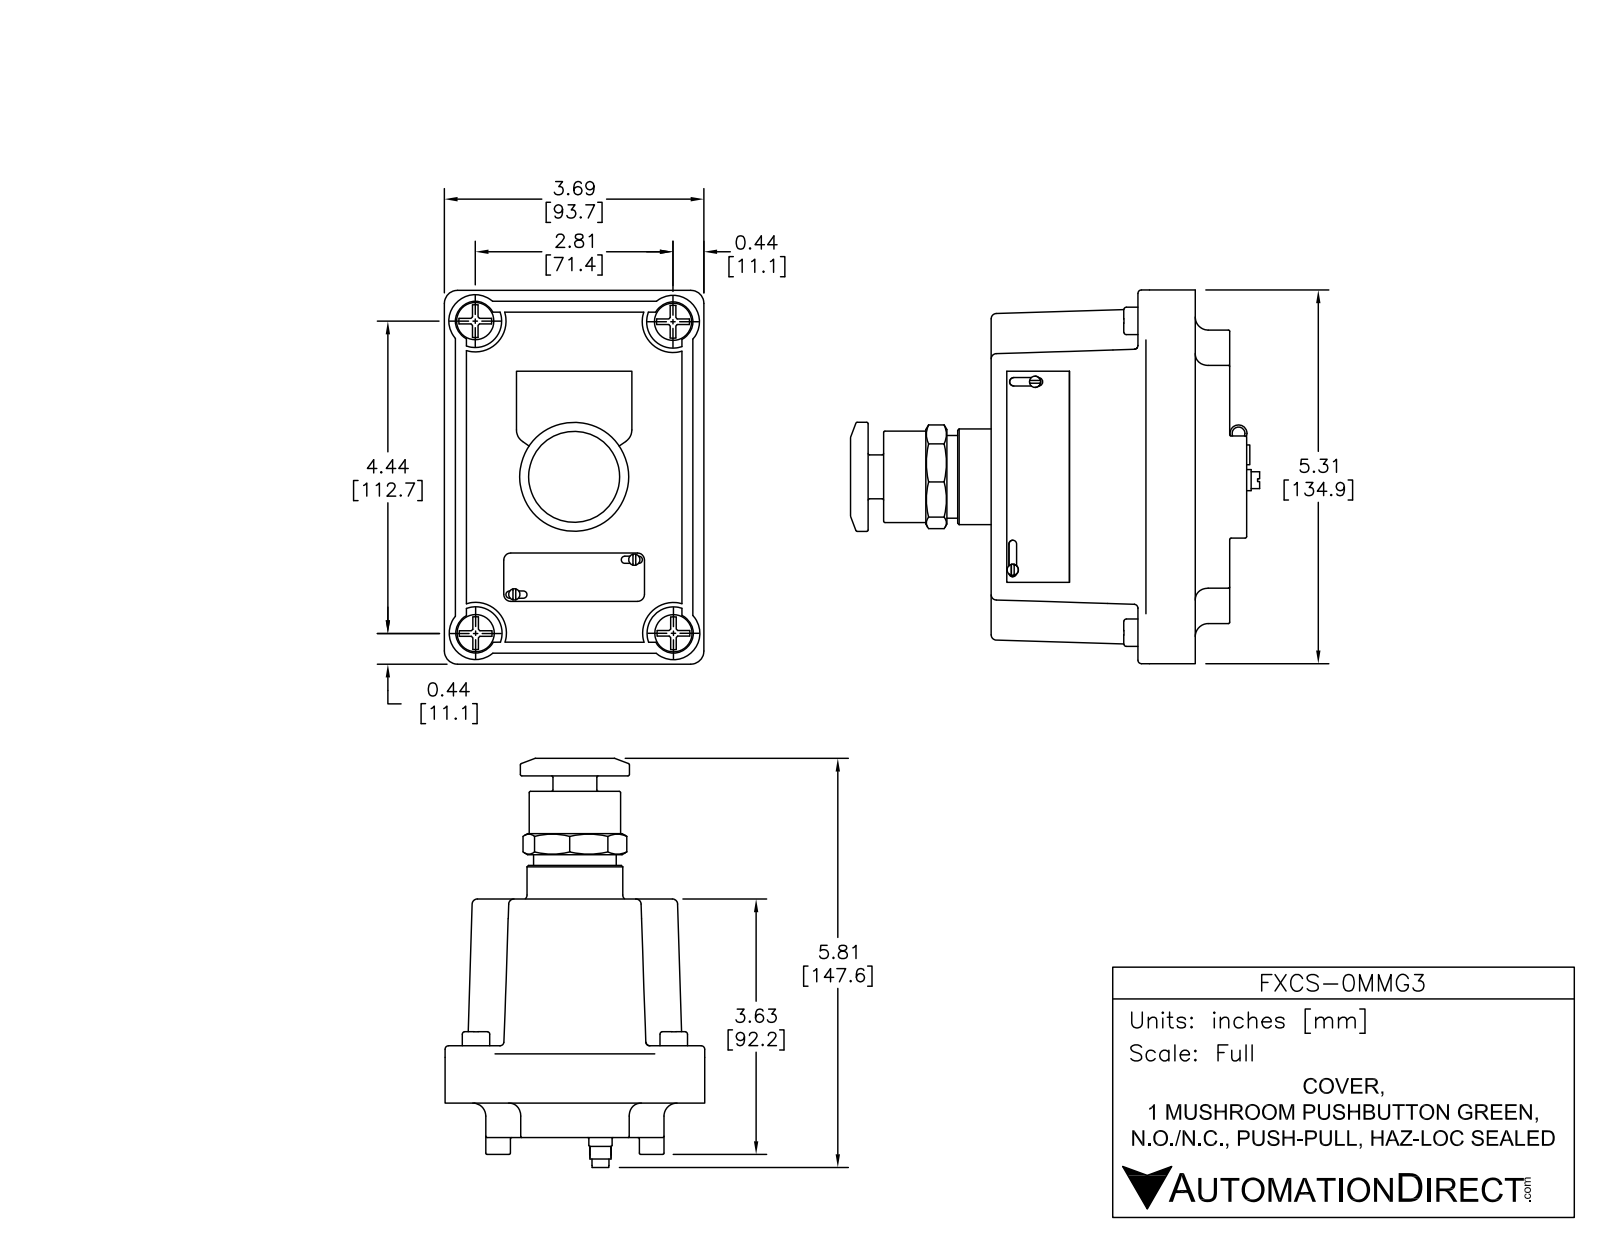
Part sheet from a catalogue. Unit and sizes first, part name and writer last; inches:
Units: inches
Overall size (bounding box): 5.814 × 5.31 × 3.69
Round holes (diameter × count): ⌀0.16 ×8, ⌀0.198 ×1
Round bosses / shafts (diameter × count): ⌀0.16 ×6, ⌀0.39 ×4, ⌀1.55 ×1, ⌀1.36 ×1, ⌀1.3 ×1, ⌀1.175 ×1, ⌀0.623 ×1, ⌀0.33 ×1
Partial cylindrical surfaces — rounded edges, fillets, slot ends (radius × count): R0.02 ×22, R0.05 ×12, R0.051 ×4, R0.055 ×4, R0.06 ×4, R0.075 ×4, R0.1 ×4, R0.185 ×4
Main face-to-face distances: 0.49, 3.39, 2.9, 0.02, 3.69, 0.578, 3.111, 1.19, 0.7, 2.2
Hole centre spacings: 0.25, 2.197, 0.5, 2.183, 2.239, 0.75, 2.308, 0.728
Volume: 50.56 in³ · Surface area: 103.2 in²
Bodies: 2 solids, 716 faces (296 planar, 155 cylindrical, 265 other)
Part name (STEP PRODUCT): FXCS-0MMG3
STEP written by: SolidWorks 2015 (AUTOMOTIVE_DESIGN)
